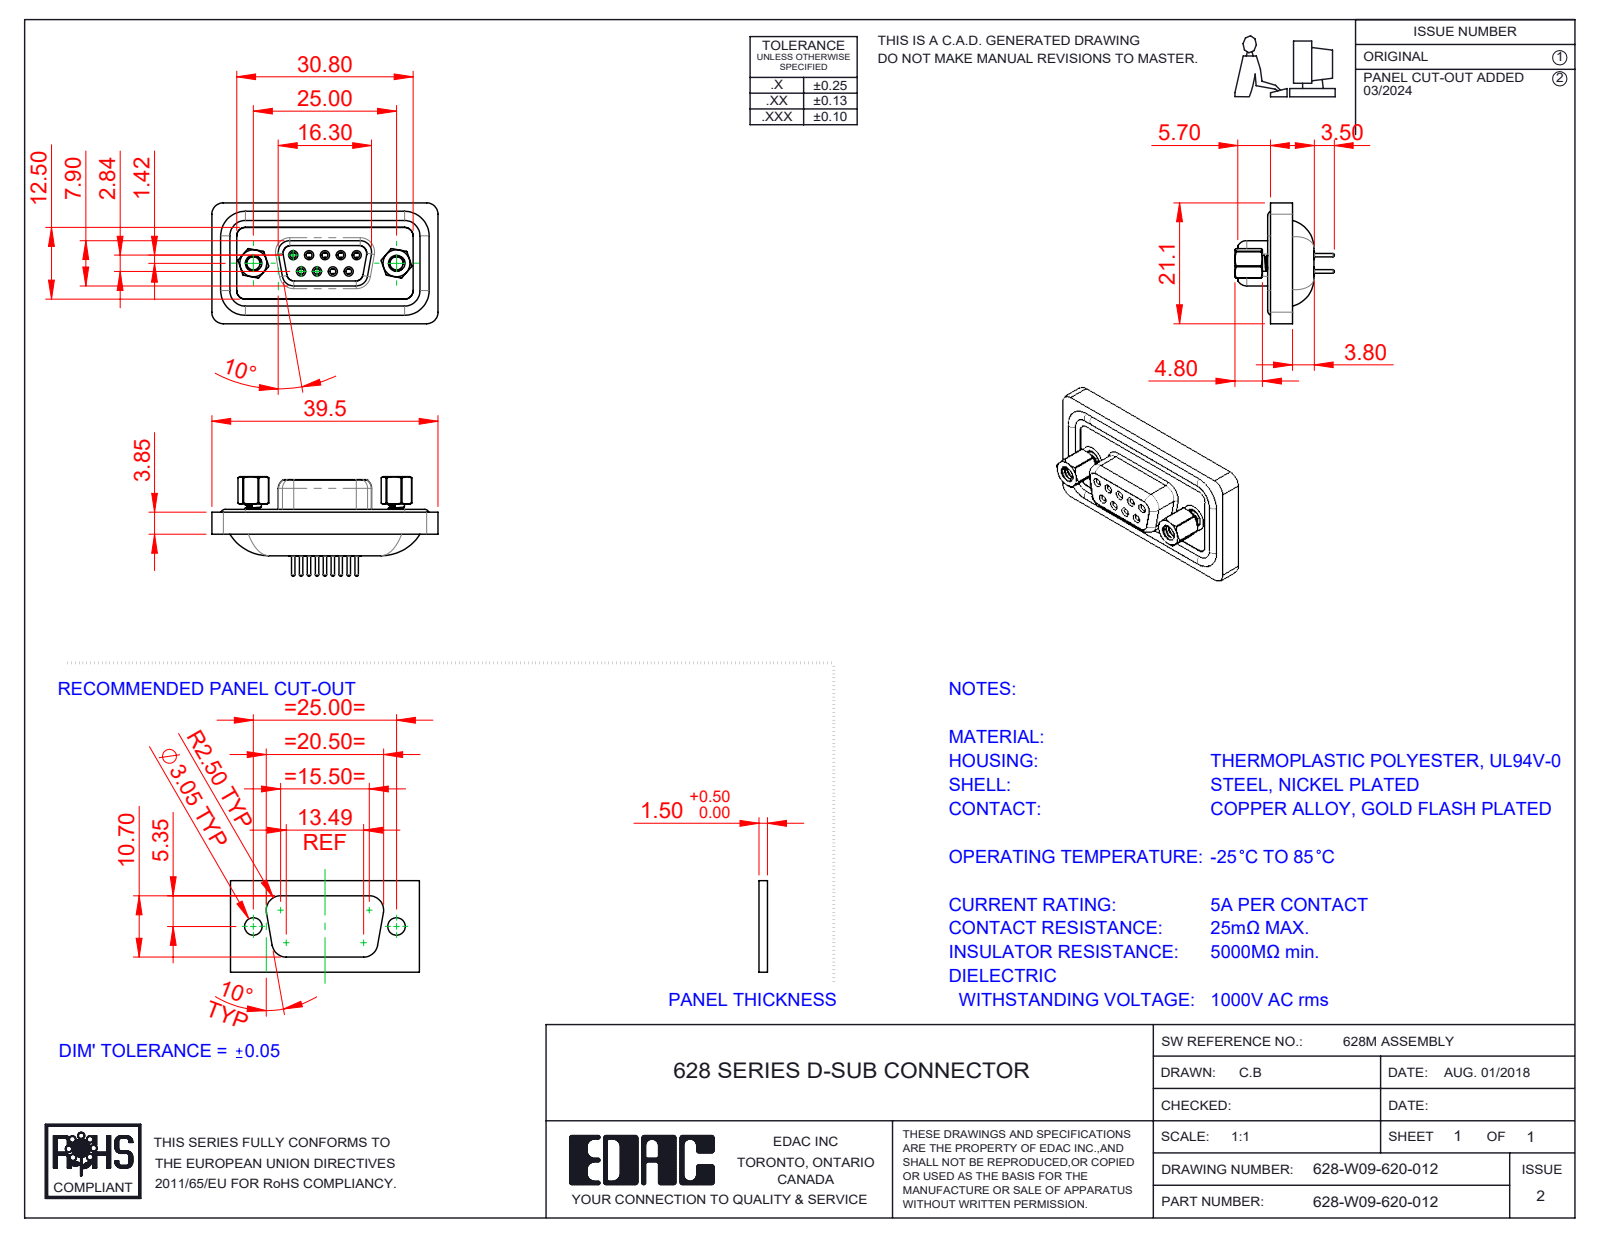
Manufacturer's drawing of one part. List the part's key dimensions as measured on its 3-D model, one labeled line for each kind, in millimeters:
Part name (STEP PRODUCT): 628W Contact Row 1_20; 628W Shell Front_09 Contacts; 628W Housing_09 Contacts; 628-W09-620-012 (+4 more)
STEP written by: SolidWorks 2020 (CONFIG_CONTROL_DESIGN)
Units: millimetres
Bodies: 17 solids, 936 faces (236 planar, 409 cylindrical, 291 other)
Overall size (bounding box): 39.5 × 21.1 × 16.85
Volume: 5 030 mm³ · Surface area: 7 419 mm²
Round holes (diameter × count): ⌀1 ×9, ⌀1.1 ×9, ⌀1.5 ×9, ⌀1.7 ×9, ⌀1.8 ×9, ⌀2 ×9, ⌀2.26 ×2, ⌀2.29 ×2, ⌀4 ×2, ⌀4.8 ×2, ⌀5 ×2
Round bosses / shafts (diameter × count): ⌀1.6 ×13, ⌀2.2 ×9, ⌀0.6 ×9, ⌀4.9 ×2, ⌀2.79 ×2
Partial cylindrical surfaces — rounded edges, fillets, slot ends (radius × count): R2 ×16, R1.5 ×14, R1.35 ×8, R2.7 ×6, R0.5 ×4, R0.9 ×4, R1.6 ×4, R1.75 ×4
Main face-to-face distances: 0.4, 1.1, 2.75, 0.5, 3.75, 1, 3.5, 3.35, 3.85, 7.5
Hole centre spacings: 3.16, 2.77, 5.54, 5.03, 5.04, 8.31, 7.1, 7.48
